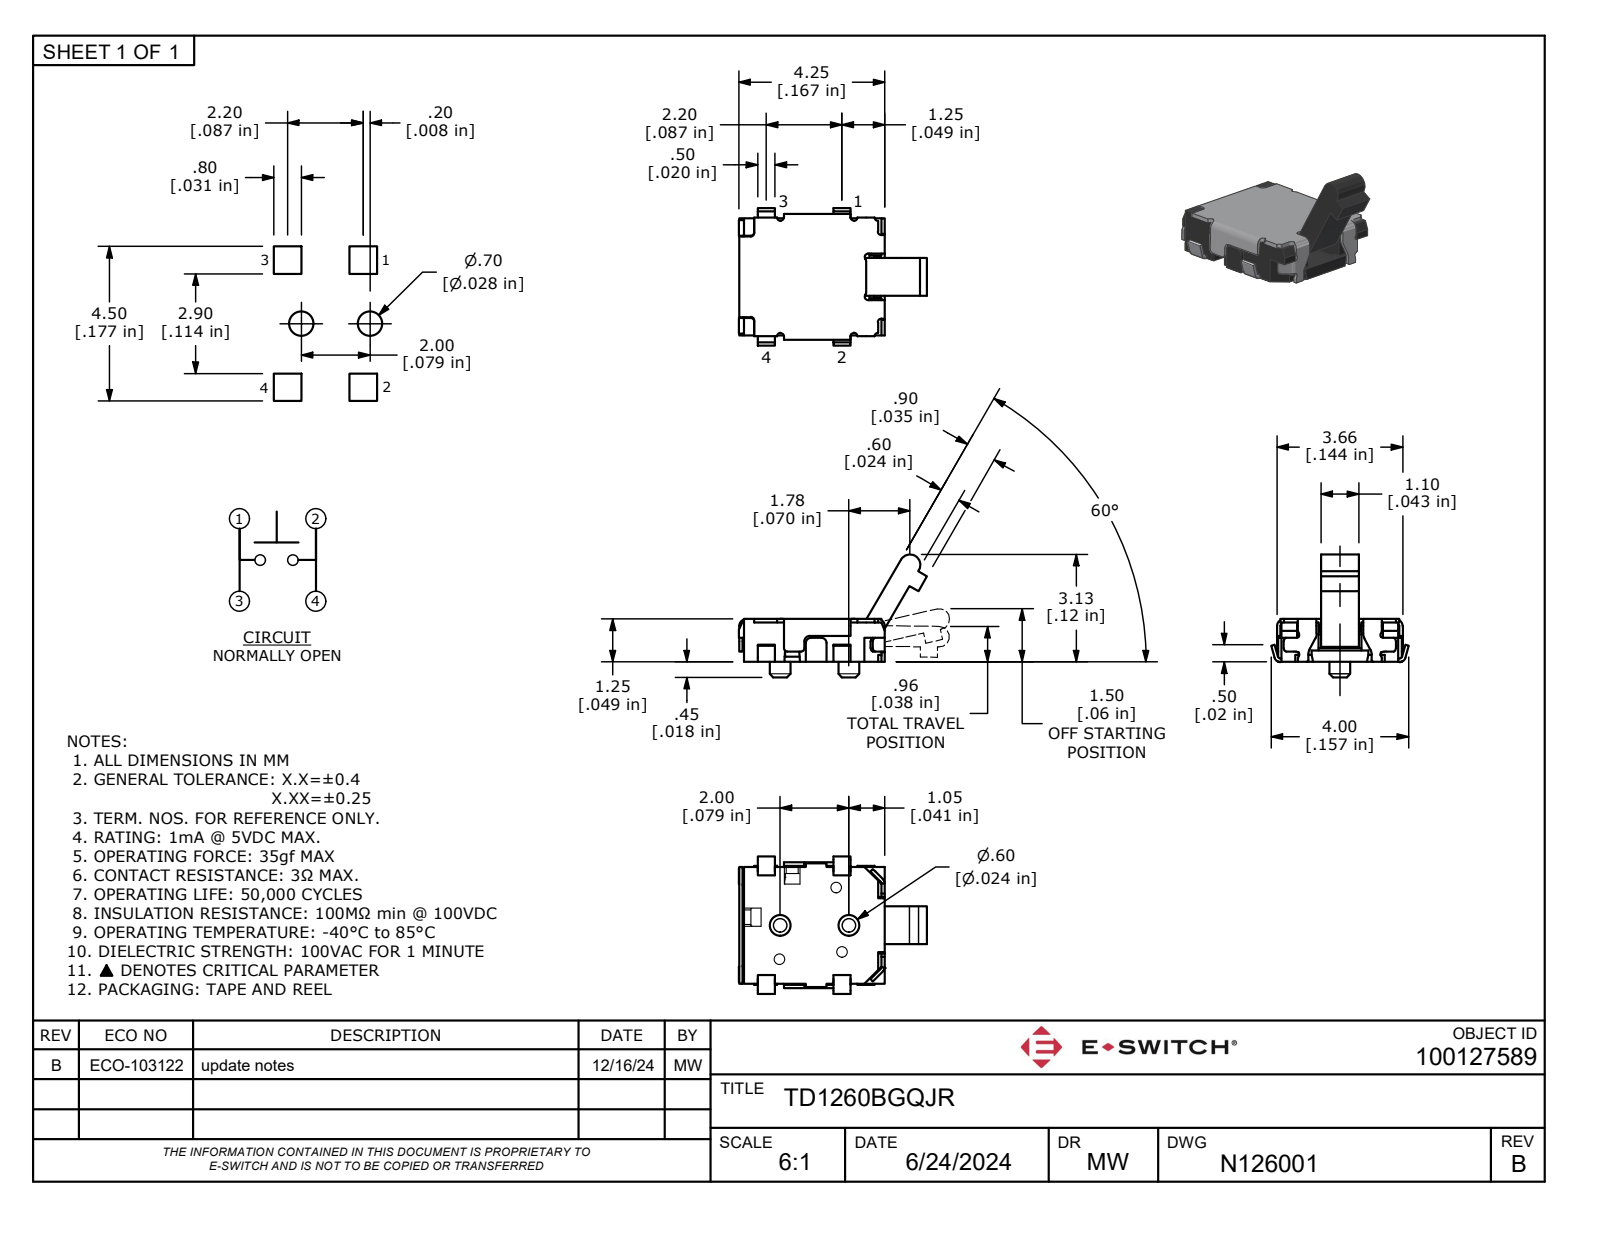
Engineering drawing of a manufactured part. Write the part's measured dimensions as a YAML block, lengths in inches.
part_name: "100127589_Simplify_1"
step_written_by: "Autodesk Inventor 2022 (AUTOMOTIVE_DESIGN)"
units: inches
bodies: {solids: 1, faces: 426, planar: 306, cylindrical: 114, other: 6}
overall_size: [0.216, 0.157, 0.141]
volume: 0.001
surface_area: 0.167
round_holes:
  - {diameter: 0.02, count: 4}
  - {diameter: 0.012, count: 3}
  - {diameter: 0.017, count: 1}
round_bosses_or_shafts:
  - {diameter: 0.024, count: 2}
  - {diameter: 0.016, count: 1}
  - {diameter: 0.008, count: 1}
partial_cylinders:
  - {radius: 0.004, count: 36}
  - {radius: 0.008, count: 15}
  - {radius: 0.012, count: 5}
  - {radius: 0.006, count: 4}
  - {radius: 0.007, count: 3}
  - {radius: 0.005, count: 1}
  - {radius: 0.014, count: 1}
  - {radius: 0.02, count: 1}
face_to_face_distances: [0.049, 0.045, 0.033, 0.016, 0.03, 0.043, 0.089, 0.134, 0.046, 0.122]
hole_center_spacings: [0.018, 0.033, 0.035, 0.072, 0.074, 0.083, 0.084, 0.085]
